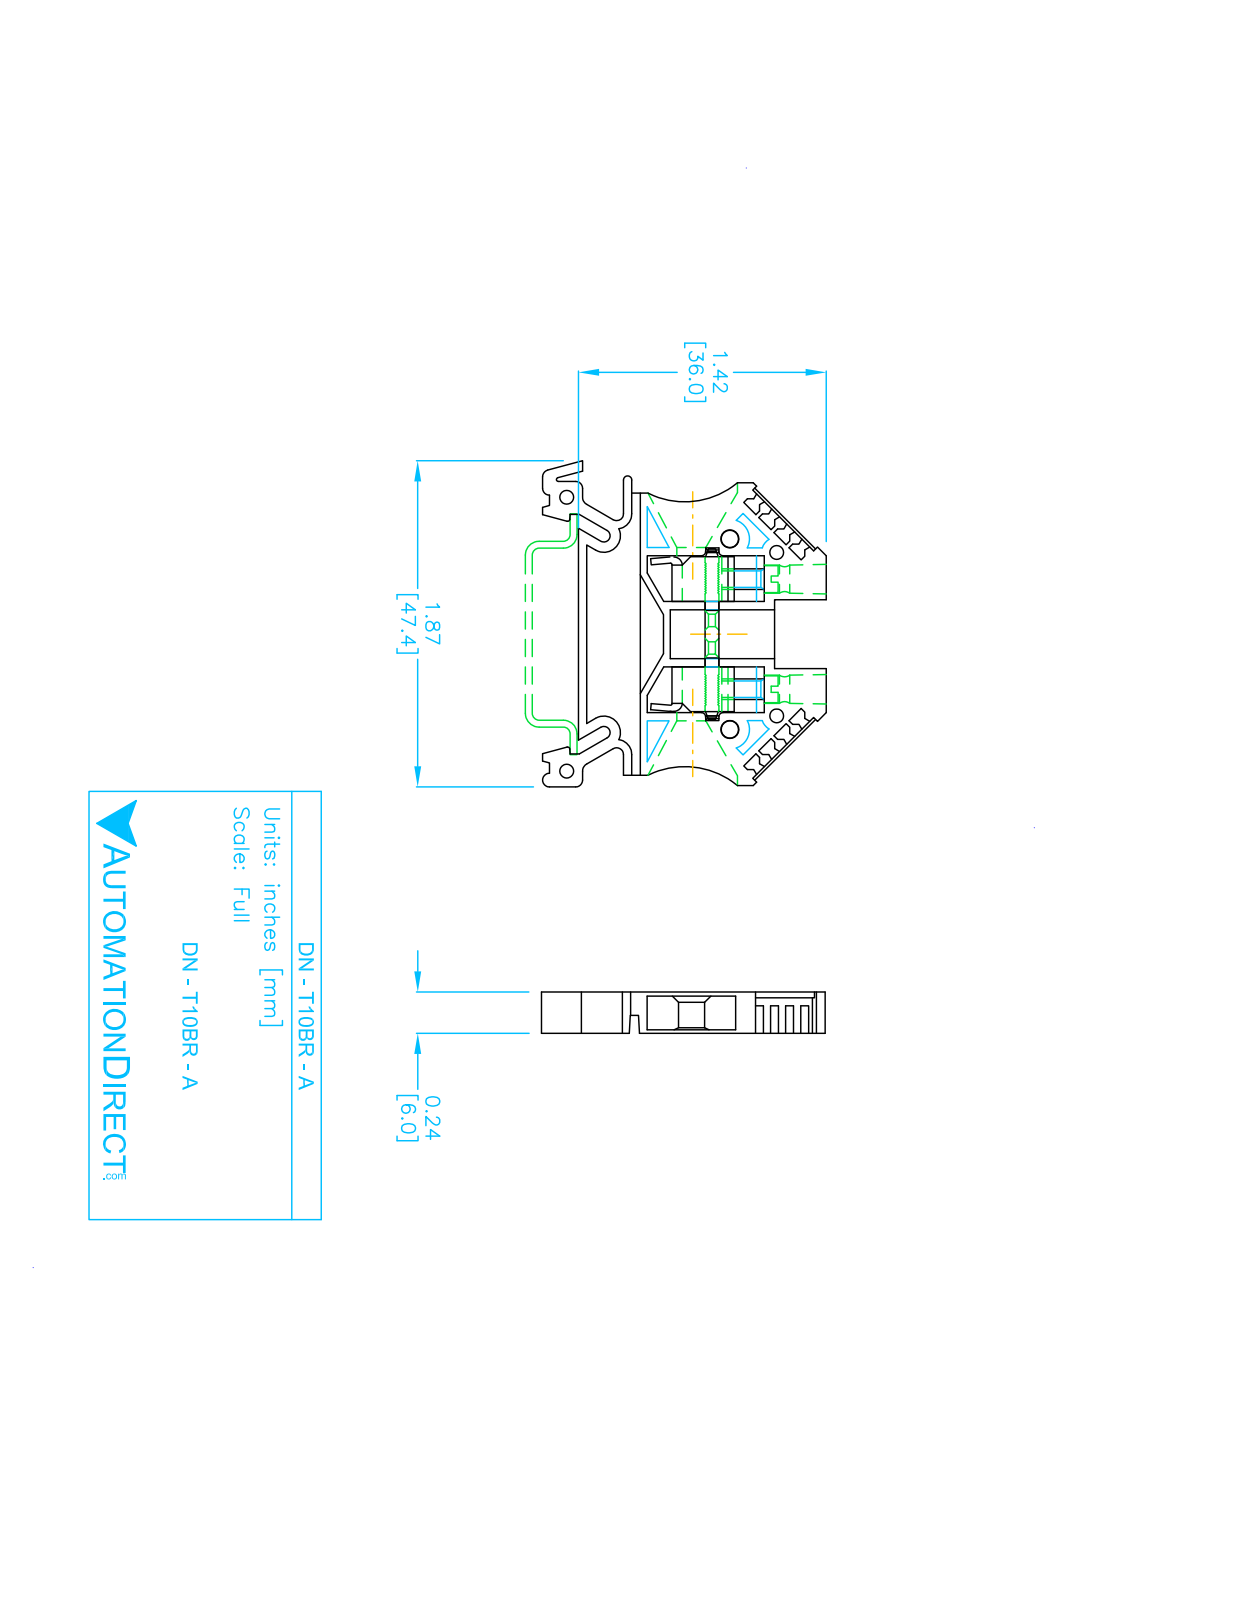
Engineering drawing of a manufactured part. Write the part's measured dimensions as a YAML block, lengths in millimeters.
part_name: "DN-T10BR-A"
step_written_by: "SolidWorks 2017 (AUTOMOTIVE_DESIGN)"
units: millimeters
bodies: {solids: 1, faces: 181, planar: 141, cylindrical: 40, other: 0}
overall_size: [47.4, 41.2, 6]
volume: 6240
surface_area: 4957
round_holes:
  - {diameter: 2, count: 2}
  - {diameter: 4.4, count: 2}
partial_cylinders:
  - {radius: 1, count: 7}
  - {radius: 0.3, count: 2}
  - {radius: 0.9, count: 2}
  - {radius: 1.2, count: 2}
  - {radius: 2.2, count: 2}
  - {radius: 2.4, count: 2}
  - {radius: 12, count: 2}
  - {radius: 0.3, count: 1}
face_to_face_distances: [5.8, 6, 3.6, 2.4, 1.2, 2.2, 3.4, 9, 1.8, 7.8]
hole_center_spacings: [16, 39.8]
